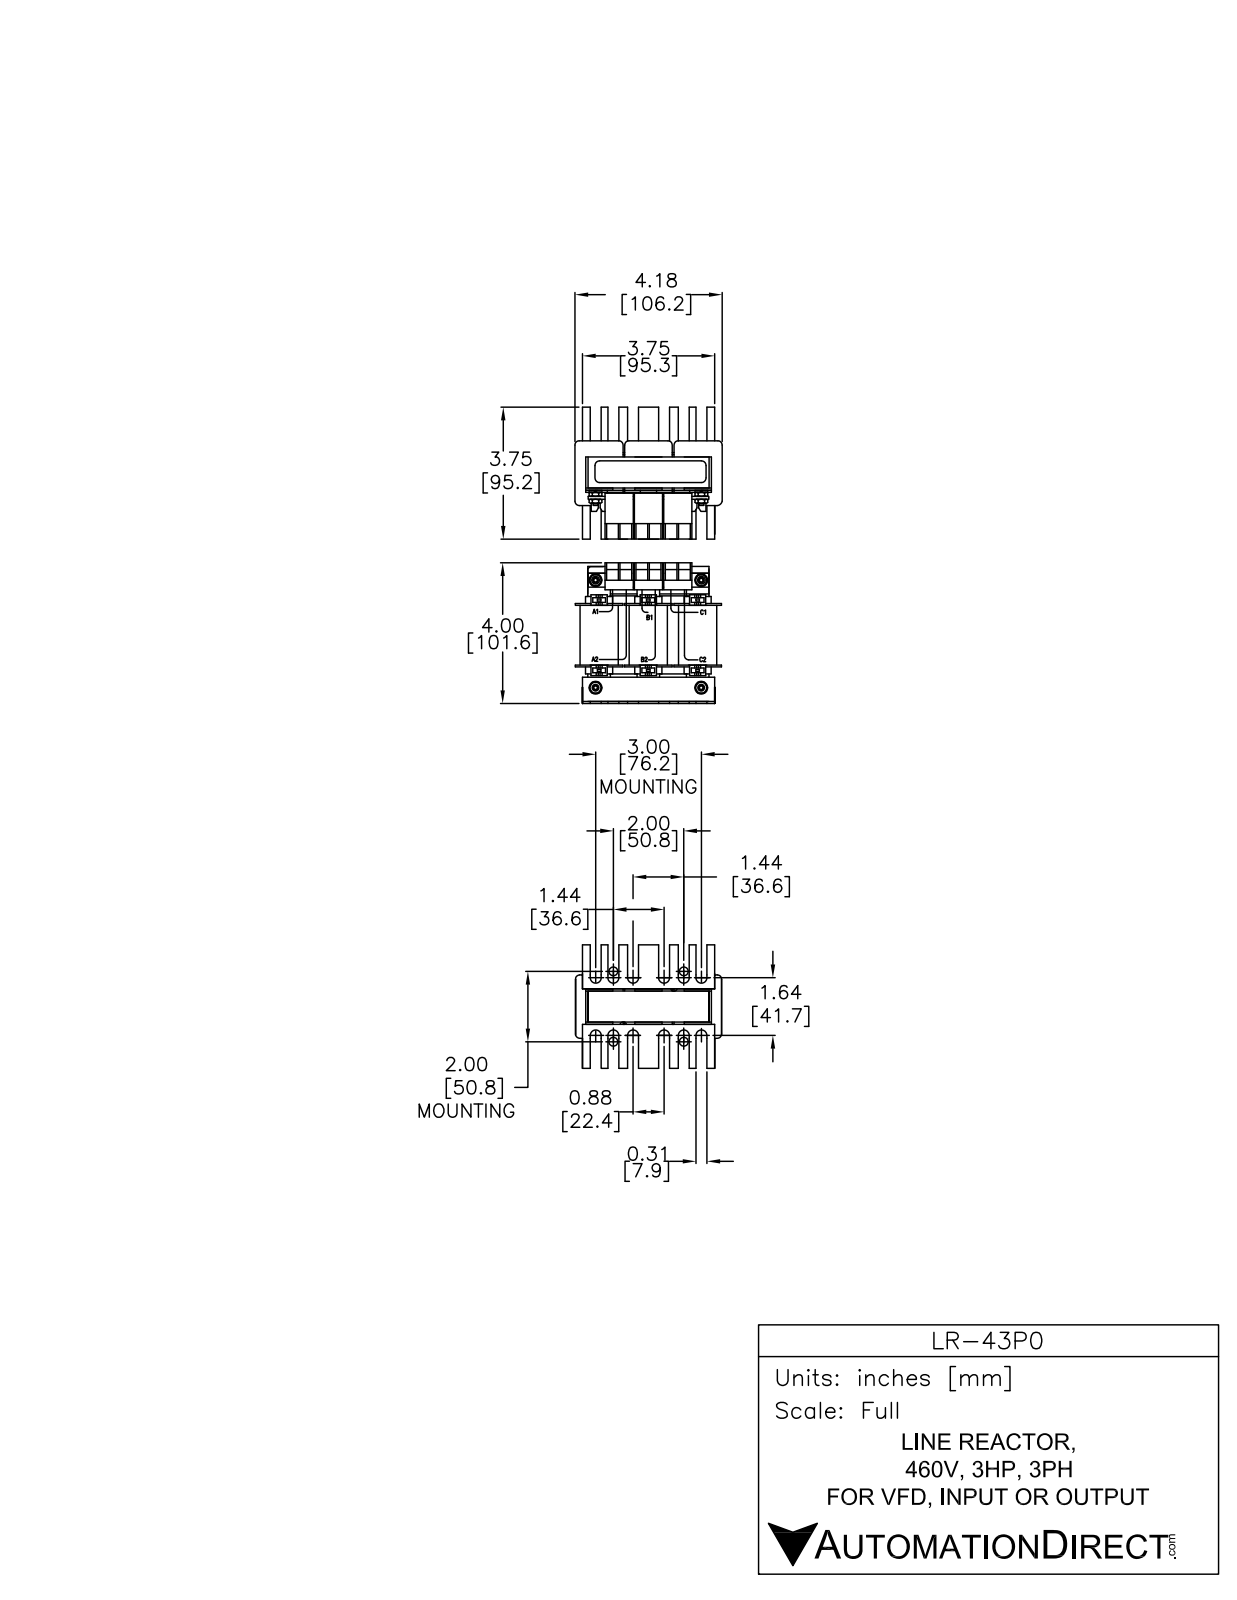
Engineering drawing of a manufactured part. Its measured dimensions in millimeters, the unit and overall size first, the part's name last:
Units: millimetres
Overall size (bounding box): 105.25 × 98.41 × 89.25
Round bosses / shafts (diameter × count): ⌀7.75 ×4, ⌀3.5 ×4
Partial cylindrical surfaces — rounded edges, fillets, slot ends (radius × count): R4 ×50, R1.82 ×24, R8 ×12, R3 ×6, R0.86 ×3, R1.25 ×2
Main face-to-face distances: 5, 21.5, 2.75, 51, 26.25, 26.5, 7.5, 29, 71, 2.5
Volume: 272 326 mm³ · Surface area: 99 223 mm²
Bodies: 17 solids, 941 faces (743 planar, 198 cylindrical, 0 other)
Part name (STEP PRODUCT): LR-43P0
STEP written by: SolidWorks 2011 (AUTOMOTIVE_DESIGN)
